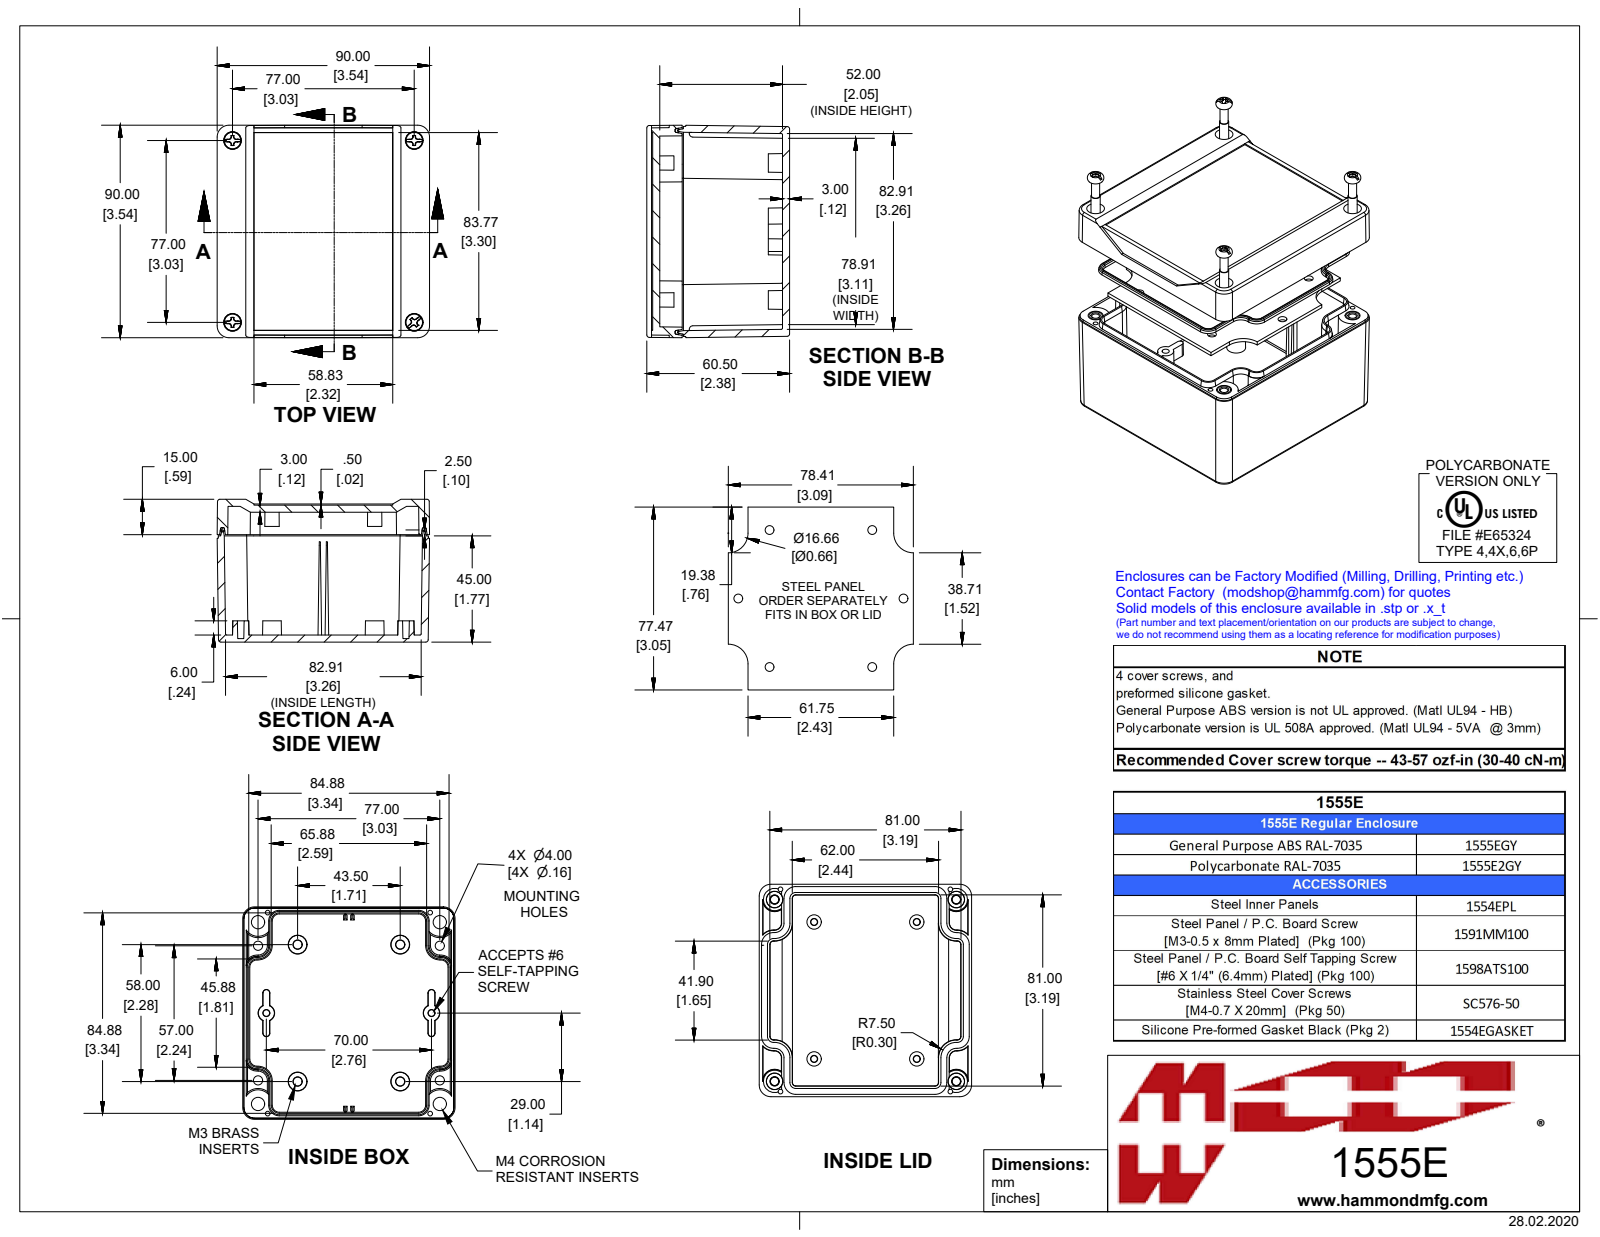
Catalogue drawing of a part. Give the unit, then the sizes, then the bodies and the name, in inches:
Units: inches
Overall size (bounding box): 3.543 × 3.543 × 2.382
Round holes (diameter × count): ⌀0.079 ×8, ⌀0.097 ×4, ⌀0.128 ×4, ⌀0.138 ×4, ⌀0.276 ×4
Round bosses / shafts (diameter × count): ⌀0.25 ×4, ⌀0.218 ×4, ⌀0.21 ×4, ⌀0.19 ×4, ⌀0.154 ×4, ⌀0.153 ×4, ⌀0.15 ×4, ⌀0.135 ×4
Partial cylindrical surfaces — rounded edges, fillets, slot ends (radius × count): R0.02 ×24, R0.039 ×8, R0.197 ×8, R0.187 ×4, R0.059 ×2
Main face-to-face distances: 0.118, 2.165, 0.059, 2.283, 2.047, 0.374, 0.492, 0.433, 0.098, 0.02
Hole centre spacings: 0.197, 0.758, 0.782, 2.338, 2.401, 2.738, 2.883, 2.938
Volume: 7.579 in³ · Surface area: 145.3 in²
Bodies: 15 solids, 1324 faces (381 planar, 317 cylindrical, 626 other)
Part name (STEP PRODUCT): 1555E2GY
STEP written by: SolidWorks 2019 (AUTOMOTIVE_DESIGN)
